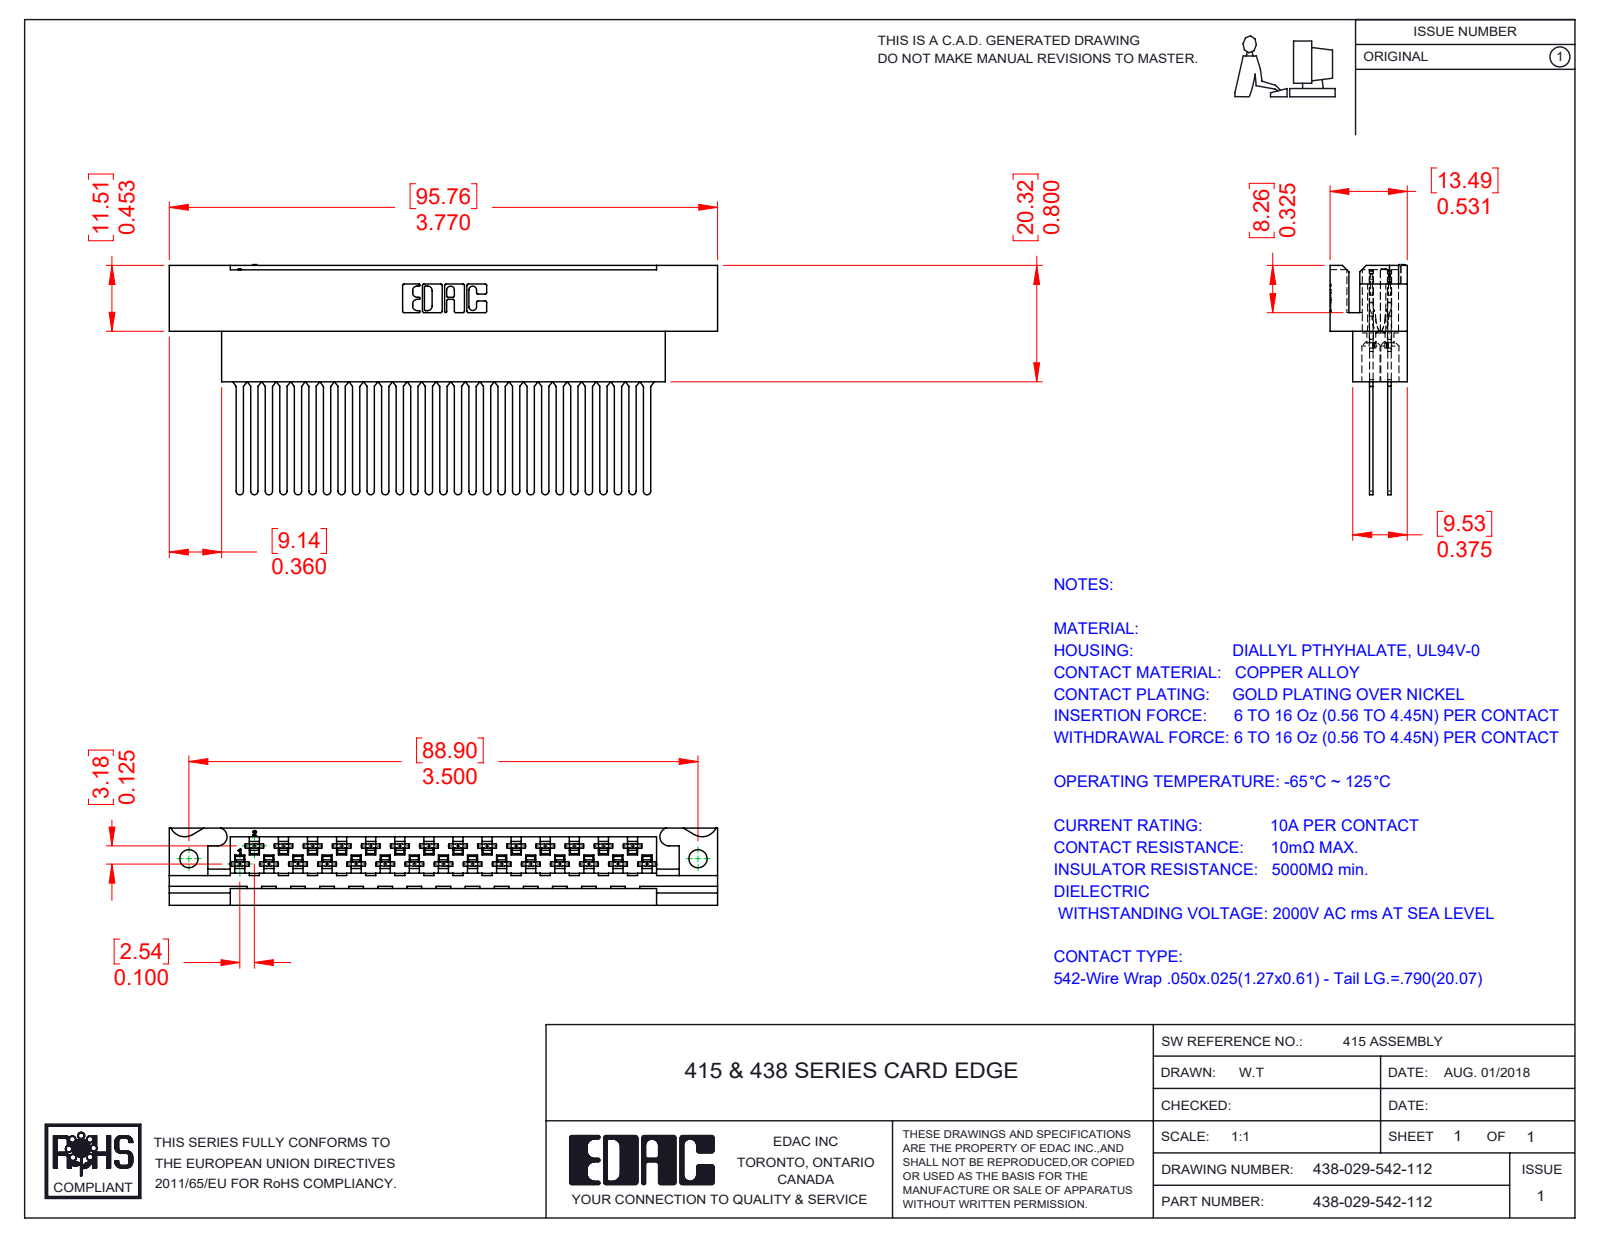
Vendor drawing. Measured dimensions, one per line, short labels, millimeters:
name: 438-029-542-112; 516-290-001_542; 438-210-001_438-210-029-112
written by: SolidWorks 2016 (CONFIG_CONTROL_DESIGN)
unit: mm
bodies: 30 solids, 2998 faces (1911 planar, 804 cylindrical, 283 other)
size: 95.76 × 40.17 × 13.49
volume: 15 894 mm³; area: 20 761 mm²
holes: 29× ⌀1.27, 29× ⌀3.3, 1× ⌀3.17, 1× ⌀3.18
rounds: 116× R0.3, 116× R0.56, 58× R0.18, 58× R0.2, 58× R0.41, 58× R2.03, 29× R0.64, 22× R0.25
face distances: 3.18, 0.61, 1.88, 7.49, 1.27, 6.61, 6, 13.49, 6.88, 2.82
hole spacings: 5.08, 10.16, 15.24, 20.32, 25.4, 30.48, 35.56, 2.54
